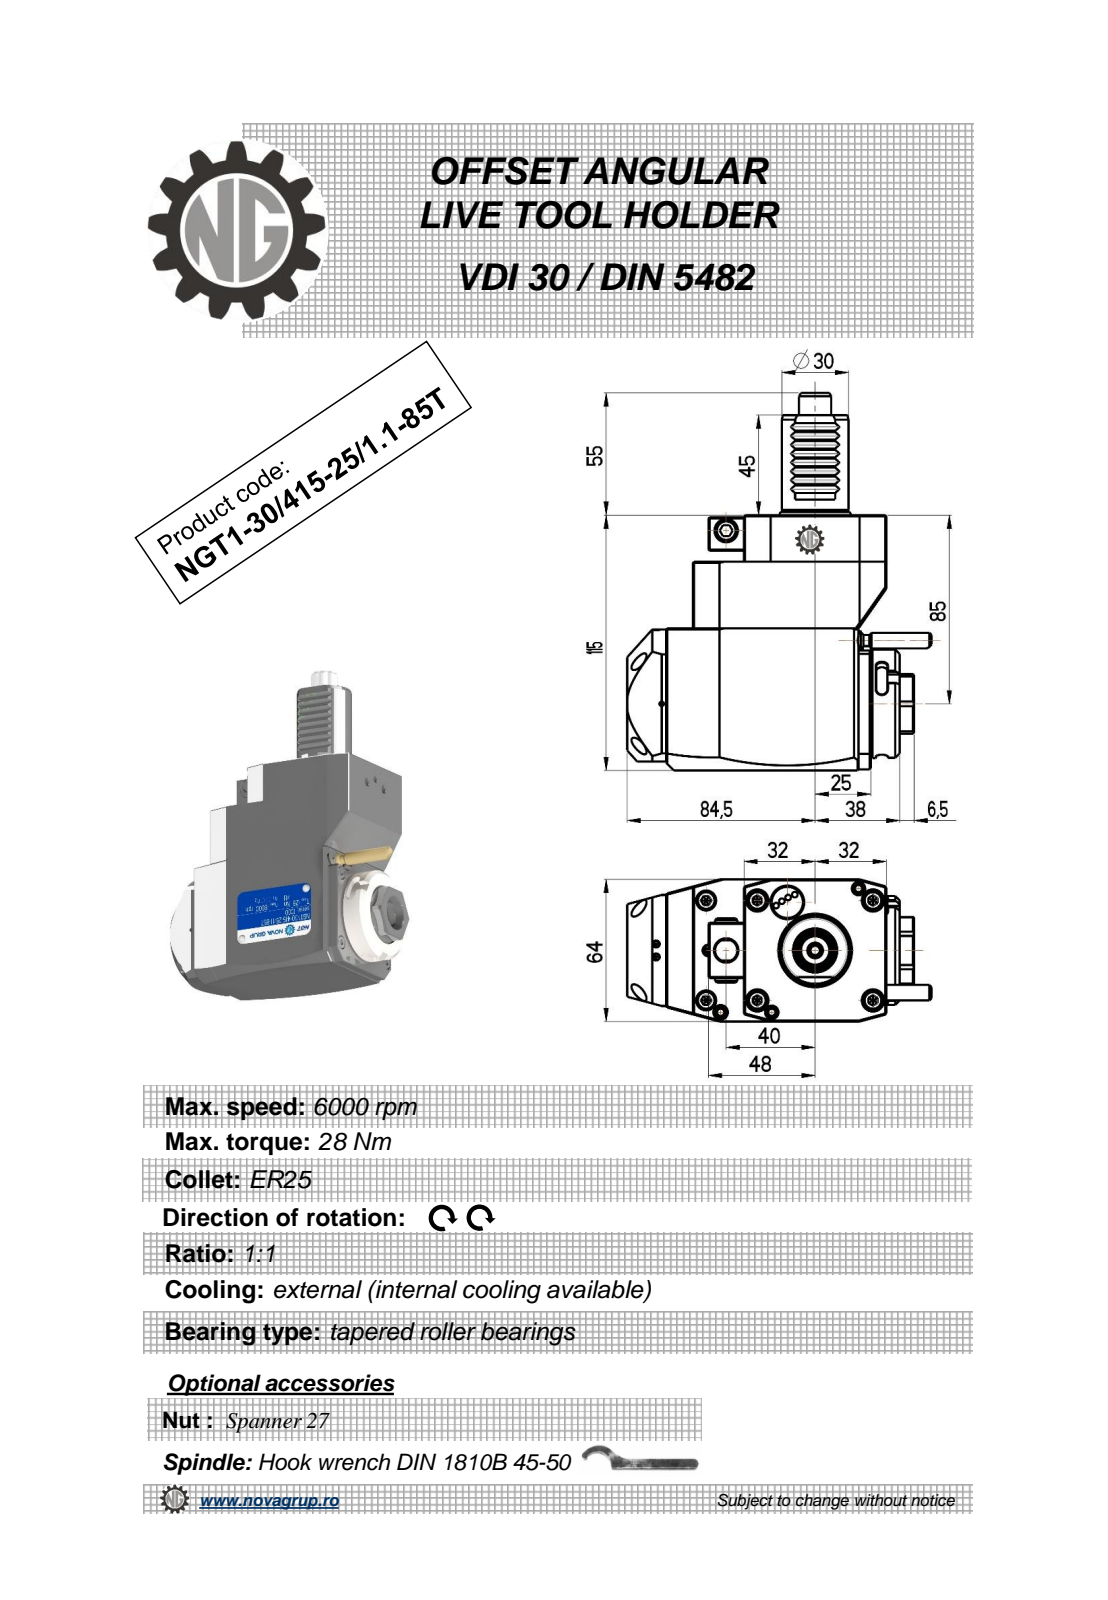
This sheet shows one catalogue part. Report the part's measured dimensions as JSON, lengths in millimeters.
{"part_name": "NGT1_30_415_25_1_1_85T", "step_written_by": "PRO/ENGINEER BY PARAMETRIC TECHNOLOGY CORPORATION, 2010280 (CONFIG_CONTROL_DESIGN)", "units": "millimeters", "bodies": {"solids": 1, "faces": 364, "planar": 178, "cylindrical": 100, "other": 86}, "overall_size": [170, 136.88, 64], "volume_mm3": 705428, "surface_area_mm2": 58679, "round_holes": [[2.5, 1], [3, 1], [4.2, 1], [5.3, 1], [8.5, 1], [9.5, 1], [10, 1], [18, 1]], "round_bosses_or_shafts": [[8.96, 2], [49, 1], [42, 1], [30, 1], [10, 1], [7, 1], [5, 1]], "partial_cylinders_radius": [[2.91, 16], [0.3, 8], [2.5, 6], [180, 2], [4.5, 1], [5.75, 1], [7.25, 1], [15, 1]], "face_to_face_distances": [64, 115, 7, 80, 87, 6, 94, 21, 116.5, 29.5], "hole_center_spacings": [34.25, 40, 51.62, 76.5]}
